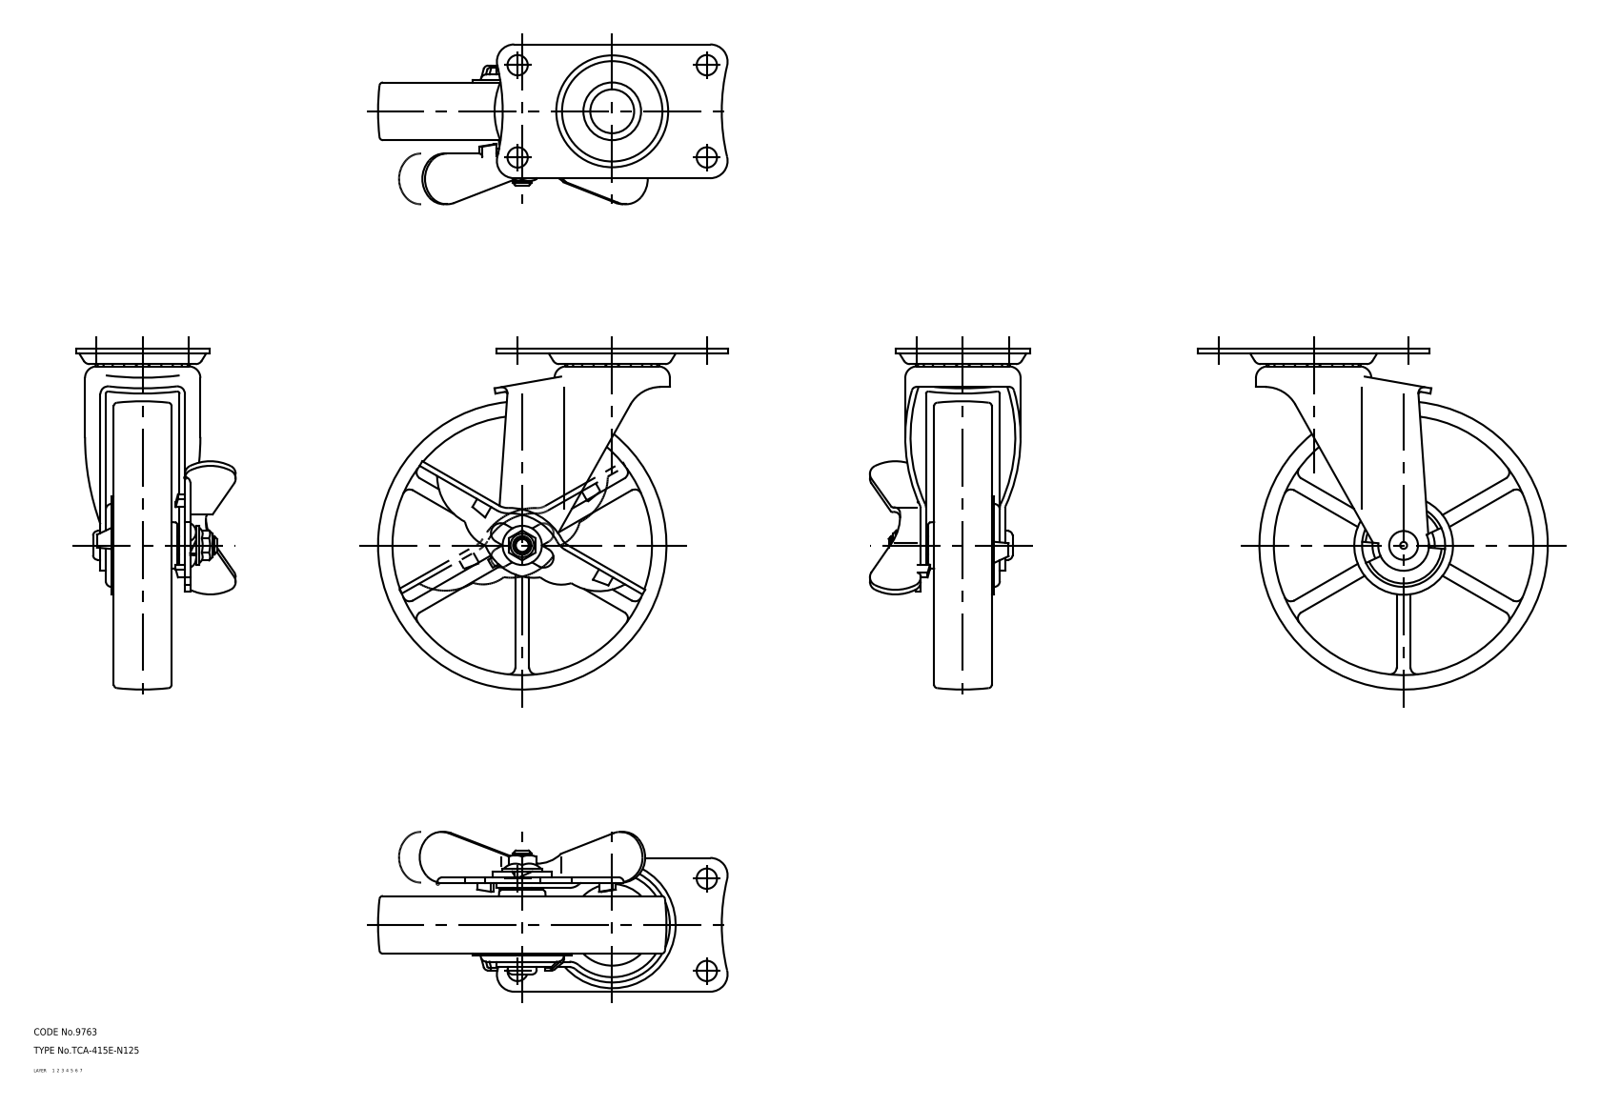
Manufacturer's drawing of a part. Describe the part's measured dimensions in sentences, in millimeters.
The part is named "wheel; mounting plate; main shaft; lever (+2 more)". Its 3-D file was written by "CADfix (AUTOMOTIVE_DESIGN)". It is 6 solids with 617 faces: 0 planar, 0 cylindrical and 617 other. Overall it measures 151.5 by 148 by 69.3 millimeters. Its volume is 274 738 cubic millimeters and its surface area 88 058 square millimeters.
